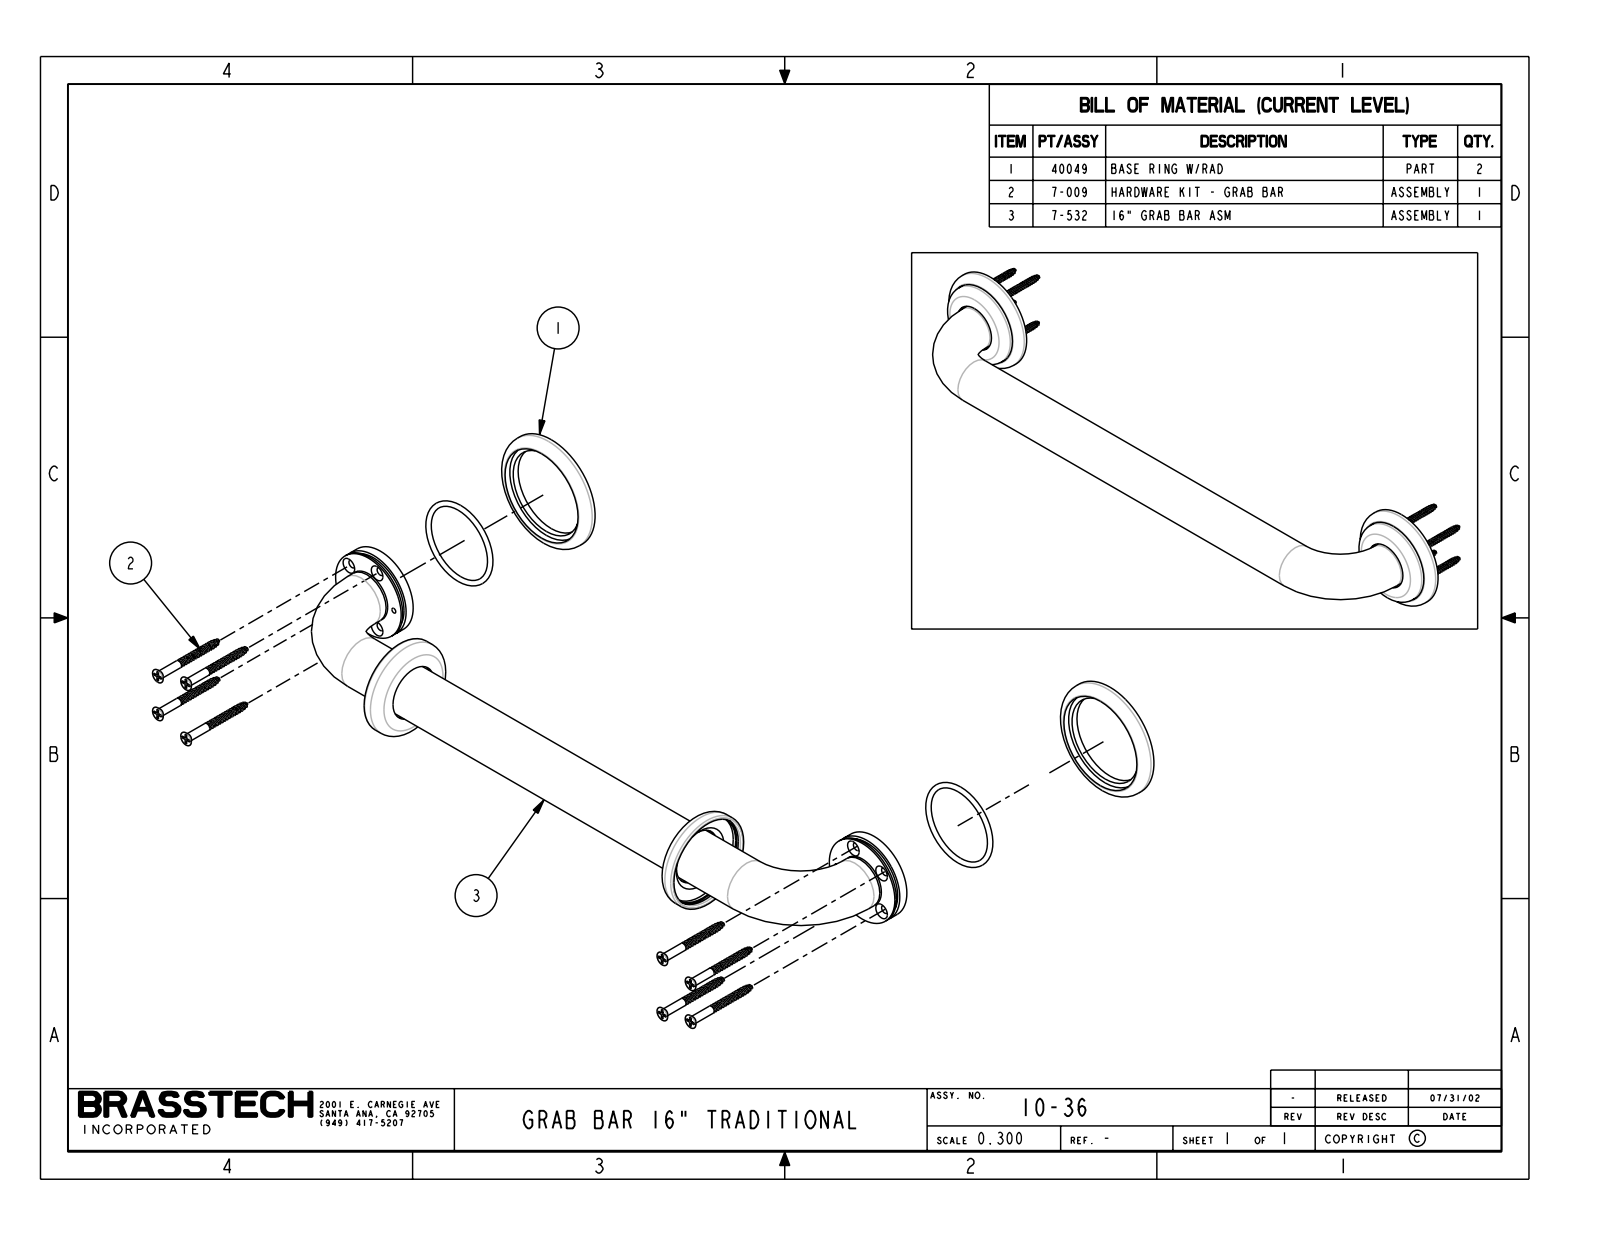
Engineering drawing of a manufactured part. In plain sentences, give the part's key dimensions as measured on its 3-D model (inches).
The part is named "10-36_SW0001". Its 3-D file was written by "PRO/ENGINEER BY PARAMETRIC TECHNOLOGY CORPORATION, 2009300 (CONFIG_CONTROL_DESIGN)". It is 0 solids with 30 faces: 8 planar, 10 cylindrical and 12 other. Overall it measures 18.845 by 3.022 by 2.845 inches. Round bosses or shafts: 2 of diameter 2.845, 2 of diameter 2.35, 1 of diameter 1.25. The main face-to-face distances are 0.313, 0.608, 0.295.
